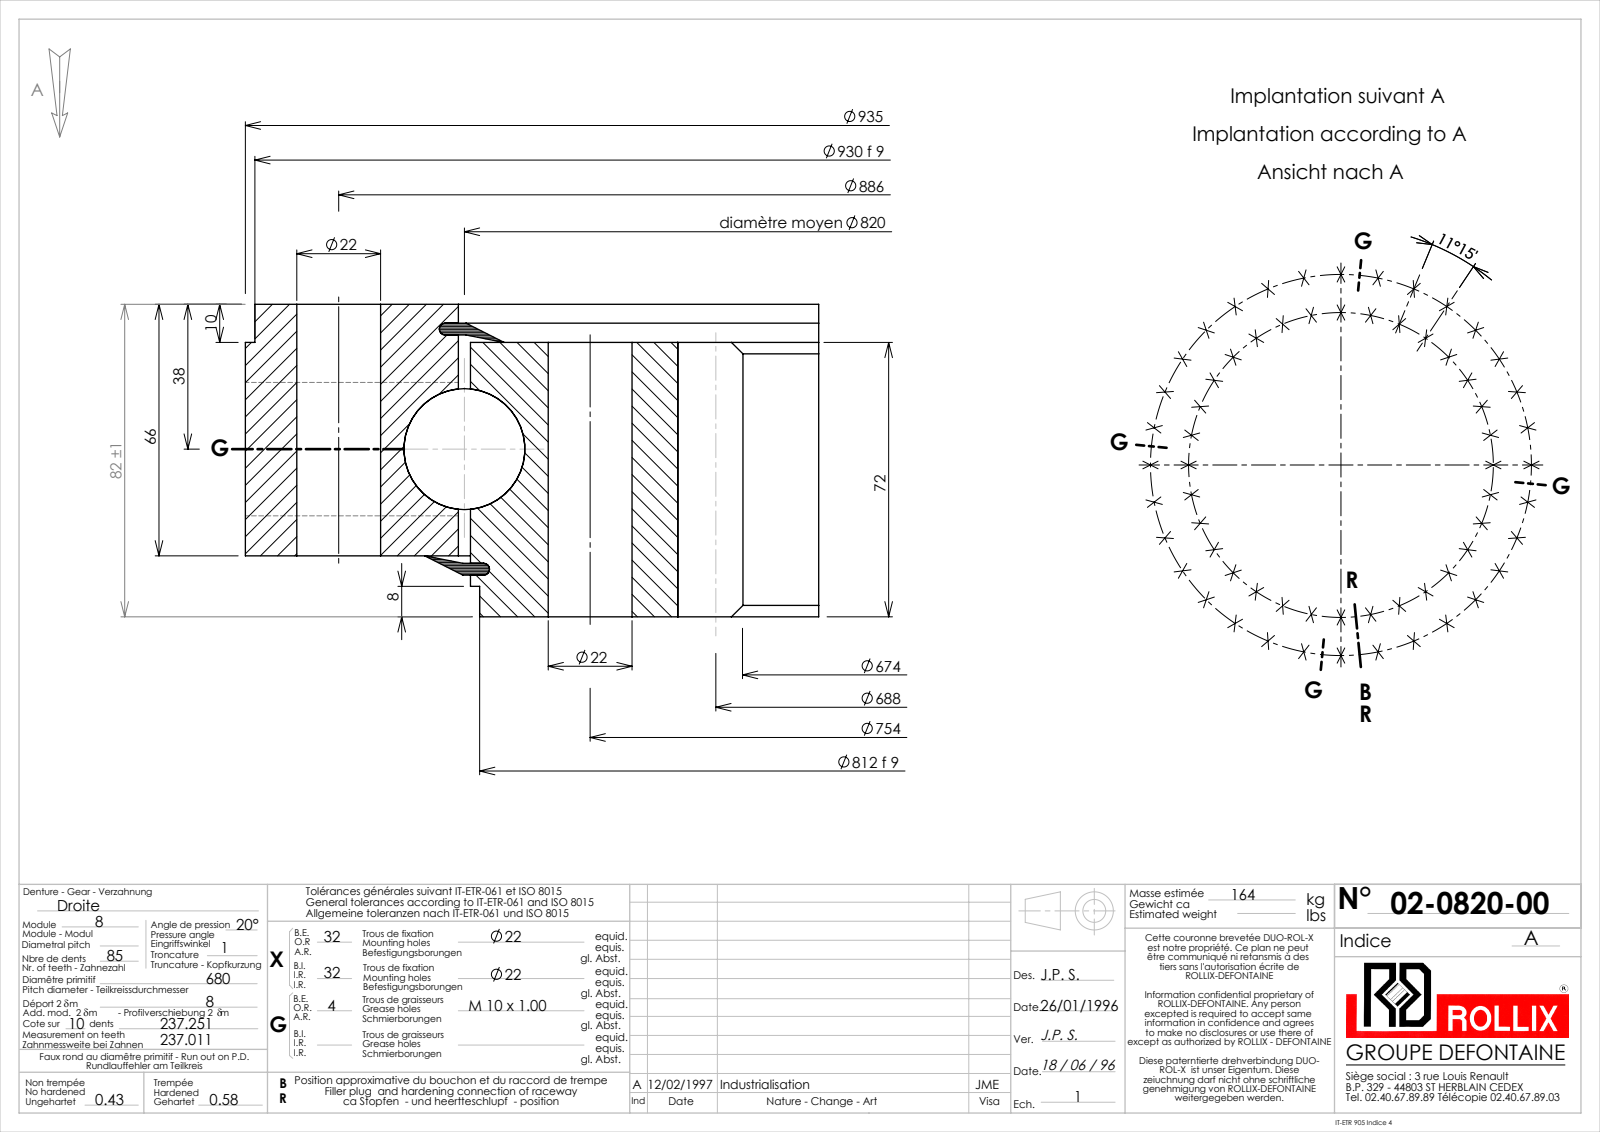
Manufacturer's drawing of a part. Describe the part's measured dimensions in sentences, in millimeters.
The part is named "02-0820-00". Its 3-D file was written by "SolidWorks 2016 (CONFIG_CONTROL_DESIGN)". It is 5 solids with 708 faces: 184 planar, 325 cylindrical and 199 other. Overall it measures 935 by 935 by 82 millimeters. Its volume is 17 550 000 cubic millimeters and its surface area 2 032 000 square millimeters. Round holes: 64 of diameter 22, 4 of diameter 9, 1 of diameter 823.17. Round bosses or shafts: 1 of diameter 935, 1 of diameter 930, 1 of diameter 816.83, 1 of diameter 812. Partial cylindrical surfaces (rounded edges, fillets, slot ends): 1 of radius 337, 1 of radius 354. The main face-to-face distances are 56, 66, 10, 16, 72, 82, 5.05, 61.05, 3.1, 1.95. The hole center spacings are 418.9, 478.33, 582.85, 739.51, 147.1, 288.54, 355.43, 626.93.
